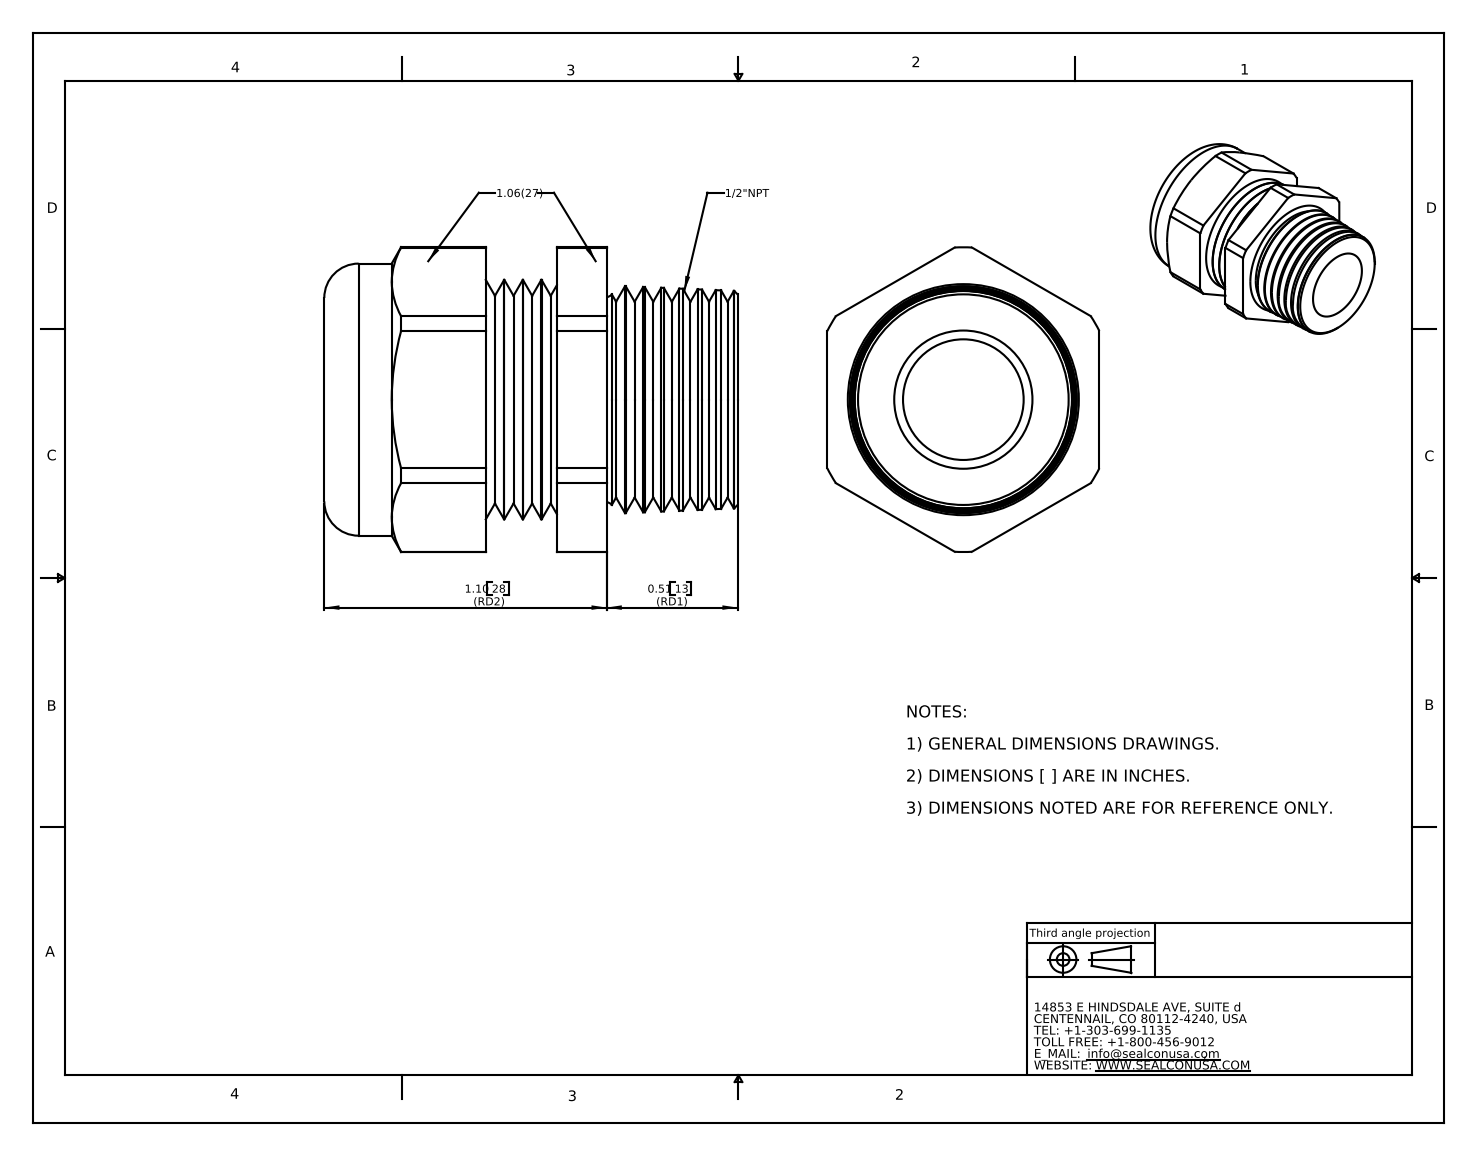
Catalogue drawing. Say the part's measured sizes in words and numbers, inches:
The part is named "CD16NR-GY". Its 3-D file was written by "SolidWorks 2007 (CONFIG_CONTROL_DESIGN)". It is 2 solids with 126 faces: 20 planar, 30 cylindrical and 76 other. Overall it measures 1.61 by 1.187 by 1.06 inches. Its volume is 0.883 cubic inches and its surface area 13.05 square inches. Round holes: 1 of diameter 0.47, 1 of diameter 0.757. Round bosses or shafts: 1 of diameter 1.06, 1 of diameter 0.933. Partial cylindrical surfaces (rounded edges, fillets, slot ends): 1 of radius 0.594. The main face-to-face distances are 1.06, 0.837, 1.347, 0.51, 0.643, 0.194, 0.704, 0.367, 0.277, 0.471.
